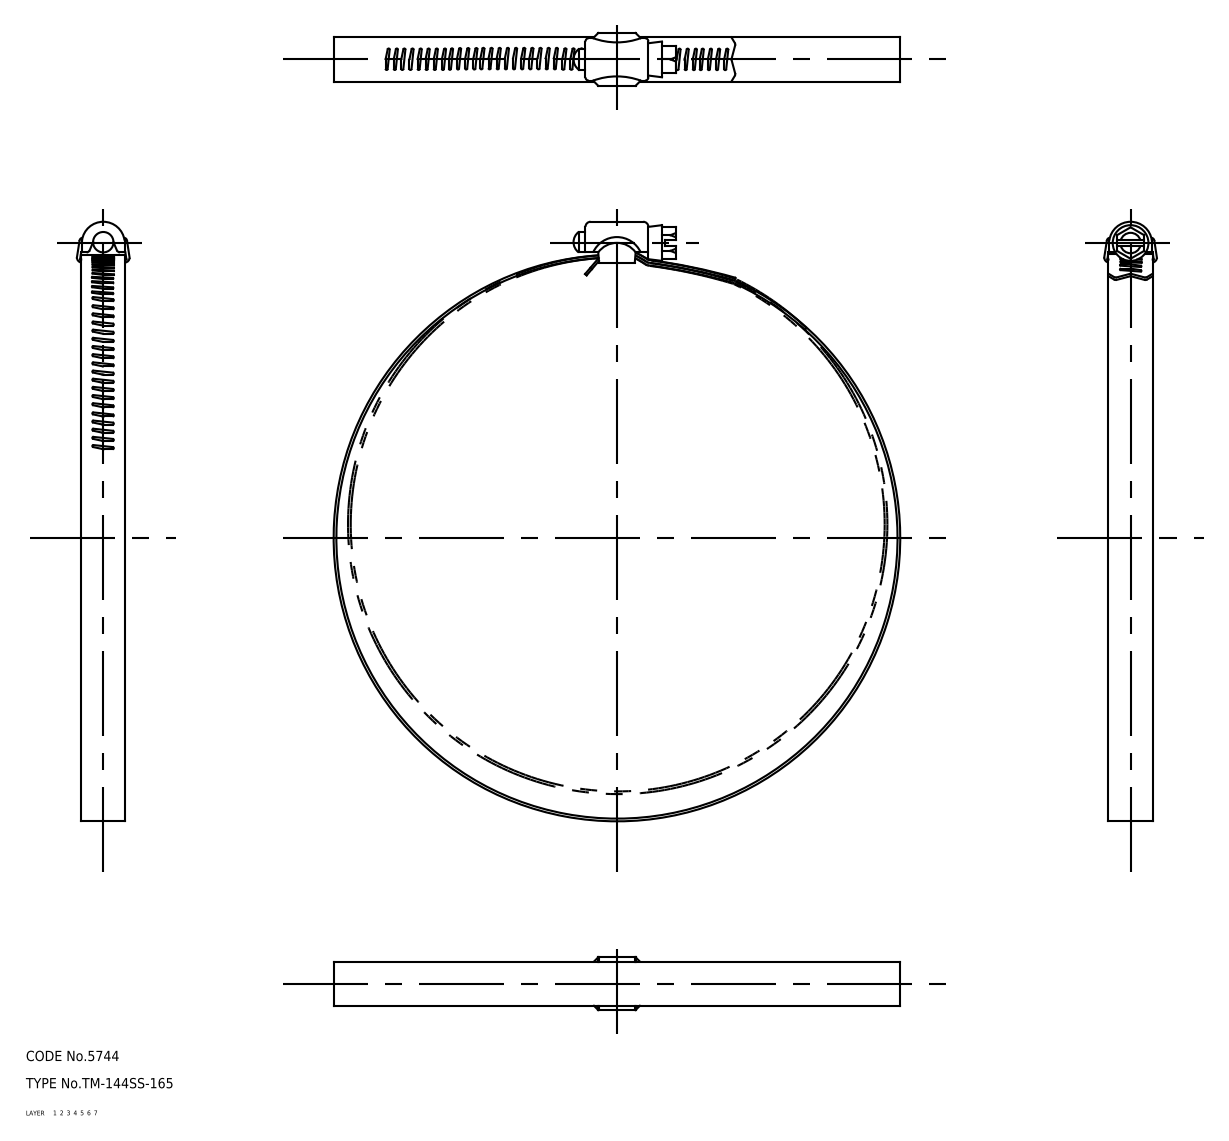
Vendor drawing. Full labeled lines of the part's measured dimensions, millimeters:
Part name (STEP PRODUCT): screw; holder; band; TM_144SS_165_19593_36
STEP written by: CADfix (AUTOMOTIVE_DESIGN)
Units: millimetres
Bodies: 3 solids, 217 faces (0 planar, 0 cylindrical, 217 other)
Overall size (bounding box): 176.3 × 166.6 × 15.63
Volume: 7 999 mm³ · Surface area: 17 866 mm²
